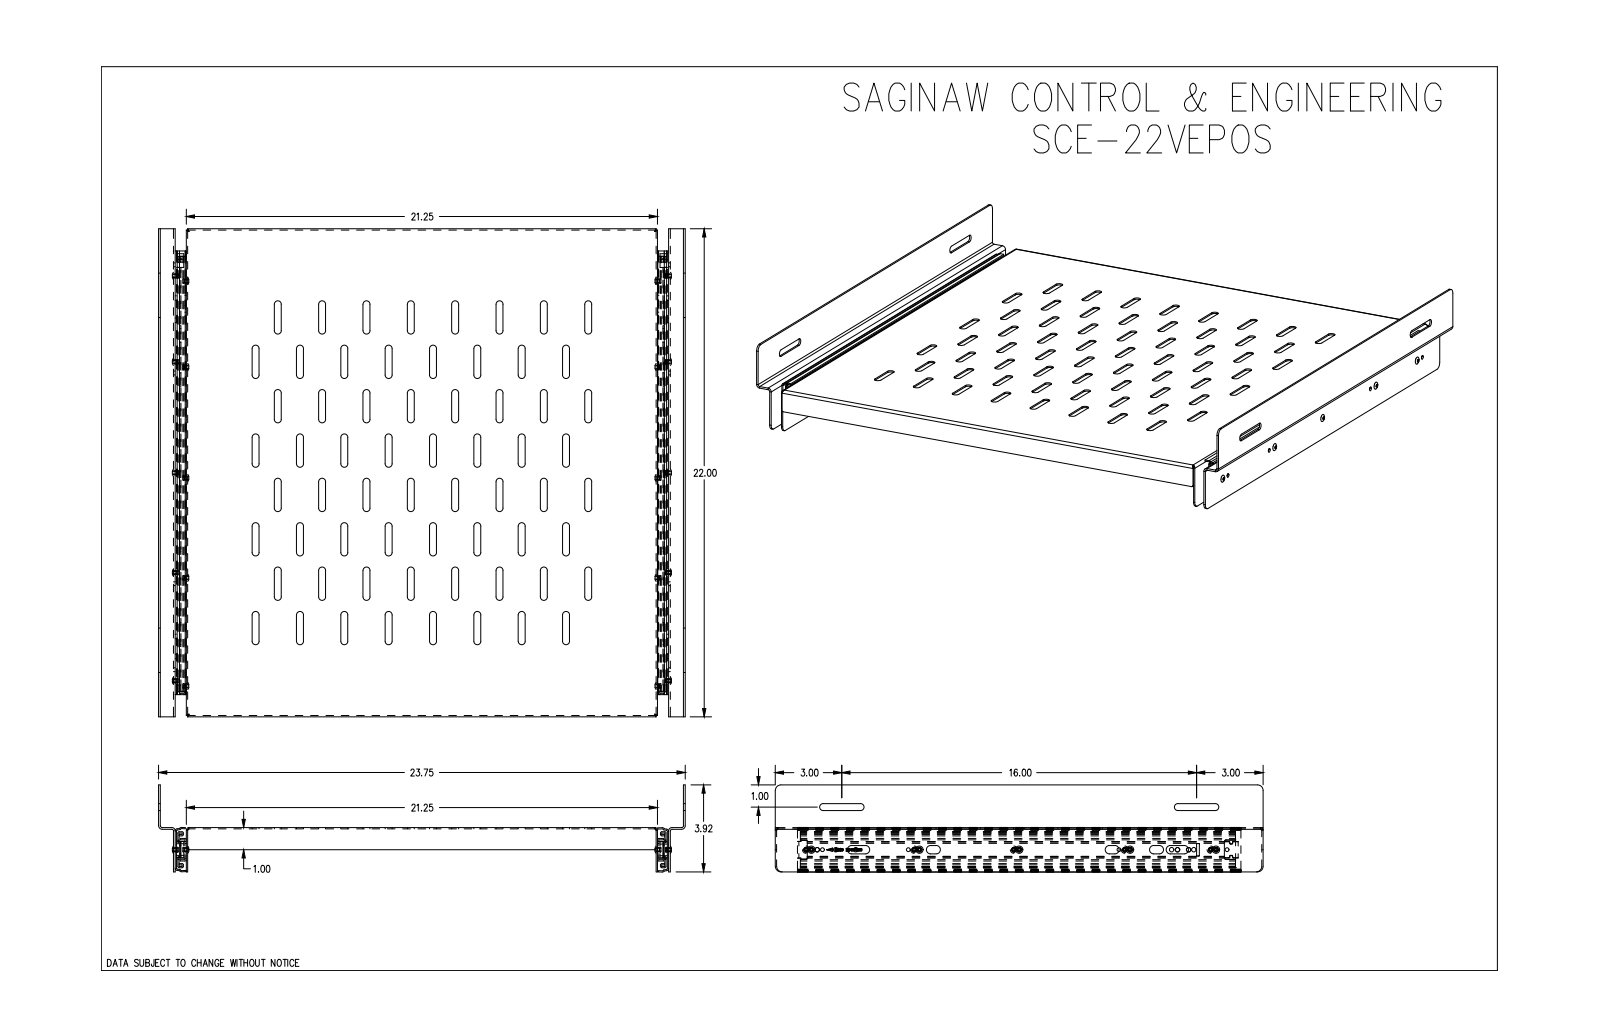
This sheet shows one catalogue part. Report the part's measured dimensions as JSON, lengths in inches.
{"part_name": "SCE-22VEPOS", "step_written_by": "SolidWorks 2021 (AUTOMOTIVE_DESIGN)", "units": "inches", "bodies": {"solids": 29, "faces": 886, "planar": 432, "cylindrical": 394, "other": 60}, "overall_size": [23.75, 22, 3.928], "volume_in3": 64, "surface_area_in2": 2083, "round_holes": [[0.2, 31], [0.172, 18], [0.097, 10]], "round_bosses_or_shafts": [[0.22, 12], [0.16, 12]], "partial_cylinders_radius": [[0.156, 132], [0.032, 20], [0.062, 16], [0.188, 10], [0.04, 8], [0.02, 4], [0.034, 4], [0.041, 4]], "face_to_face_distances": [0.06, 0.078, 0.672, 23, 0.5, 21.75, 0.055, 0.56, 21.69, 21.19], "hole_center_spacings": [0.235, 0.5, 18.25, 0.265, 3.875, 4.375, 4.5, 4.875]}
